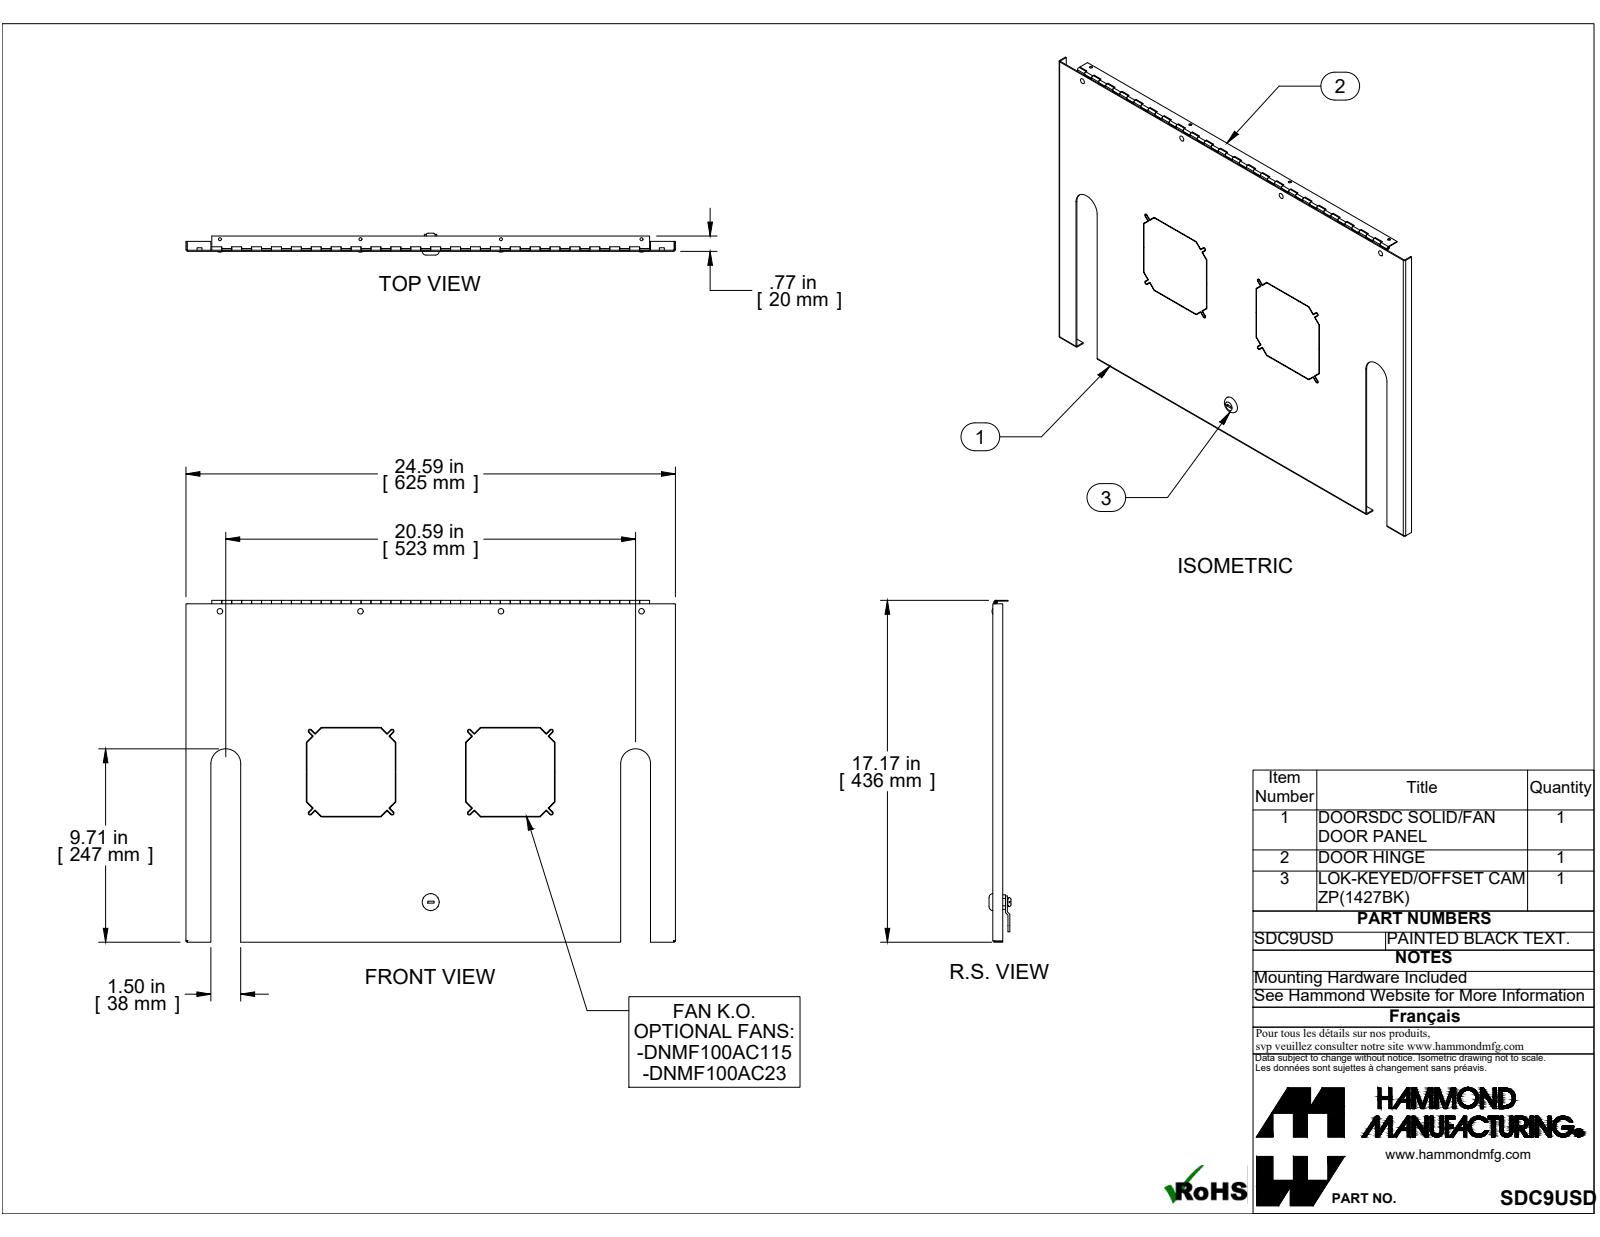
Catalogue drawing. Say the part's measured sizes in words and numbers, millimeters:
The part is named "SDC9USD". Its 3-D file was written by "SolidWorks 2019 (CONFIG_CONTROL_DESIGN)". It is 15 solids with 570 faces: 412 planar, 142 cylindrical and 16 other. Overall it measures 624.7 by 436.2 by 27.9 millimeters. Its volume is 422 100 cubic millimeters and its surface area 596 500 square millimeters. Round holes: 8 of diameter 3.8, 4 of diameter 3.2, 1 of diameter 2.3, 1 of diameter 3.2, 1 of diameter 5.2, 1 of diameter 15.2. Round bosses or shafts: 1 of diameter 18.5, 1 of diameter 5.9, 1 of diameter 4.4, 1 of diameter 2. Partial cylindrical surfaces (rounded edges, fillets, slot ends): 8 of radius 1.6, 8 of radius 2.4, 3 of radius 0.7, 3 of radius 2.2, 2 of radius 7.9, 2 of radius 19.1, 1 of radius 9.7. The main face-to-face distances are 1.4, 1, 1.4, 623.2, 2.5, 433.7, 434.8, 435.2, 436.2, 621.8. The hole center spacings are 179.4, 358.8, 179.4, 381.7, 419.7, 458.3, 490.4, 538.1.
